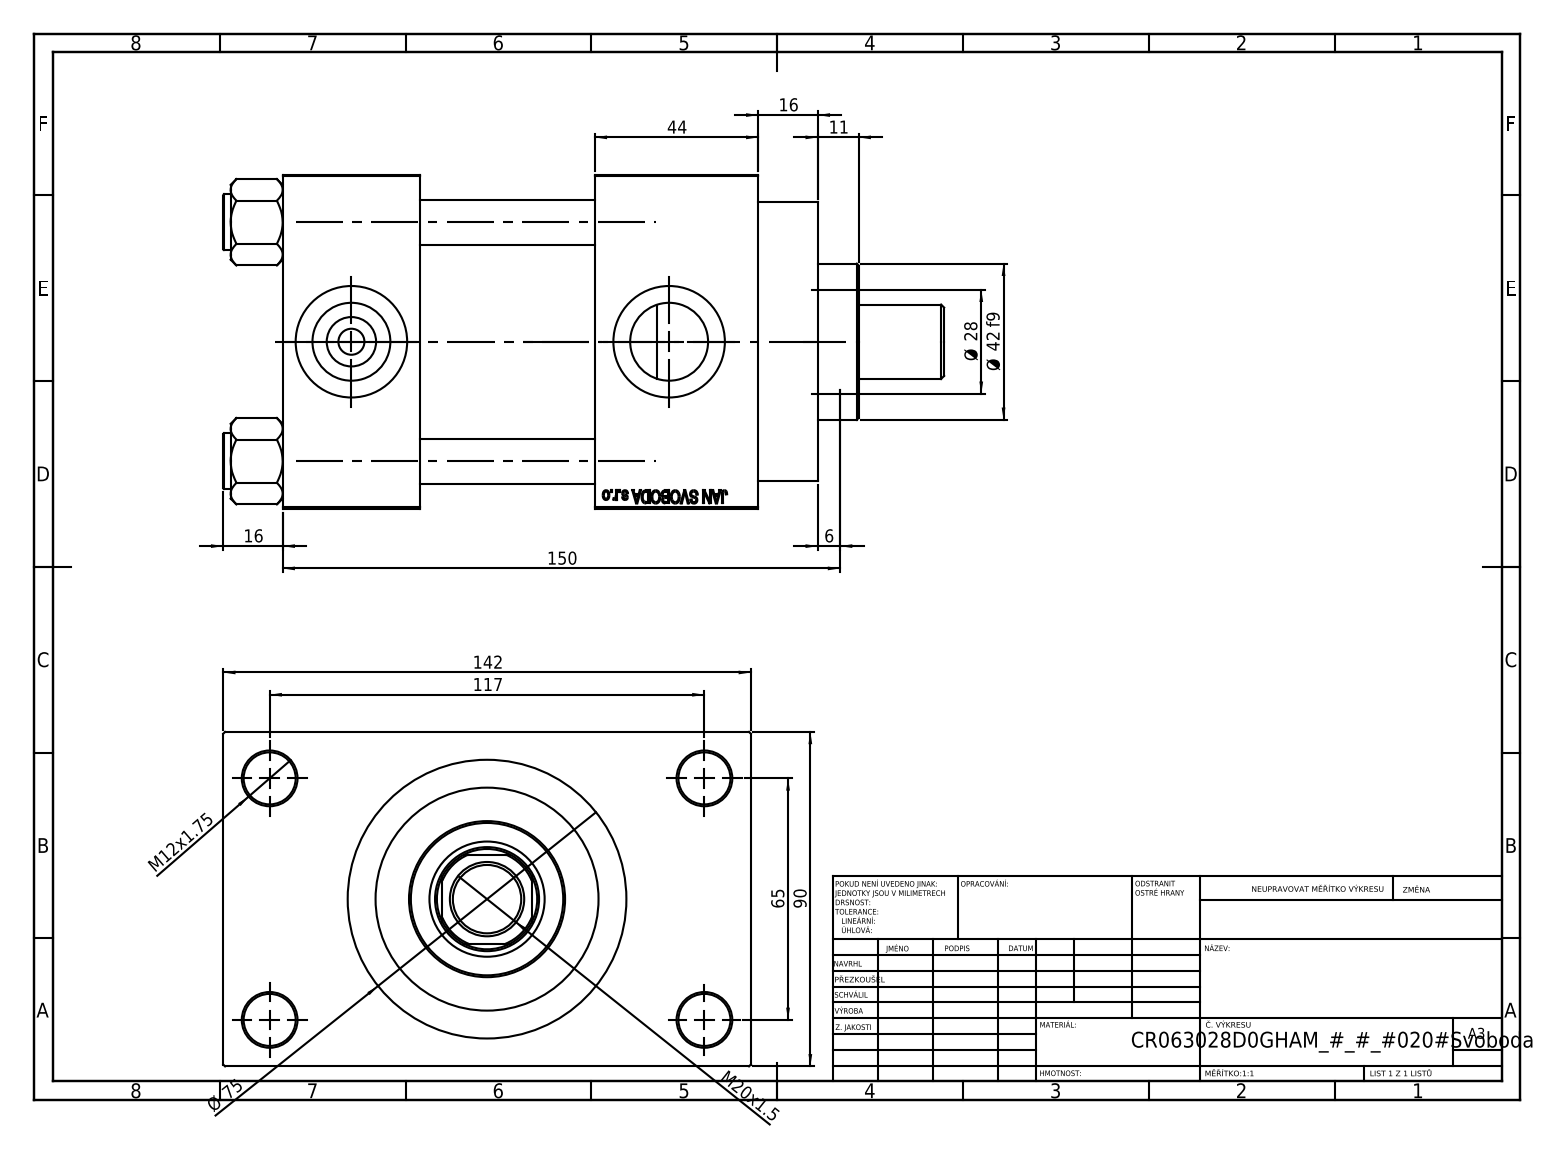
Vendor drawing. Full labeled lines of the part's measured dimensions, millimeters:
Part name (STEP PRODUCT): V215CR_D_Body; NUT_M5_D; V215CR_D_TYCINKA; ROD_END_AH (+2 more)
STEP written by: SolidWorks 2019 (CONFIG_CONTROL_DESIGN)
Units: millimetres
Bodies: 12 solids, 1117 faces (501 planar, 92 cylindrical, 524 other)
Overall size (bounding box): 194 × 142 × 90
Volume: 1 030 000 mm³ · Surface area: 188 823 mm²
Round holes (diameter × count): ⌀12 ×4, ⌀14 ×4, ⌀7 ×2, ⌀20.96 ×2, ⌀30 ×2, ⌀18.5 ×1, ⌀28 ×1, ⌀31 ×1, ⌀50 ×1, ⌀60 ×1, ⌀63 ×1
Round bosses / shafts (diameter × count): ⌀15 ×4, ⌀75 ×1, ⌀69 ×1, ⌀42 ×1, ⌀20 ×1, ⌀18 ×1
Partial cylindrical surfaces — rounded edges, fillets, slot ends (radius × count): R13.5 ×1
Main face-to-face distances: 90, 47, 84, 37, 91, 128, 44, 26, 116, 64
Hole centre spacings: 26.35, 45.47, 64.3, 66.92, 69.81, 90.65, 111.34, 65
